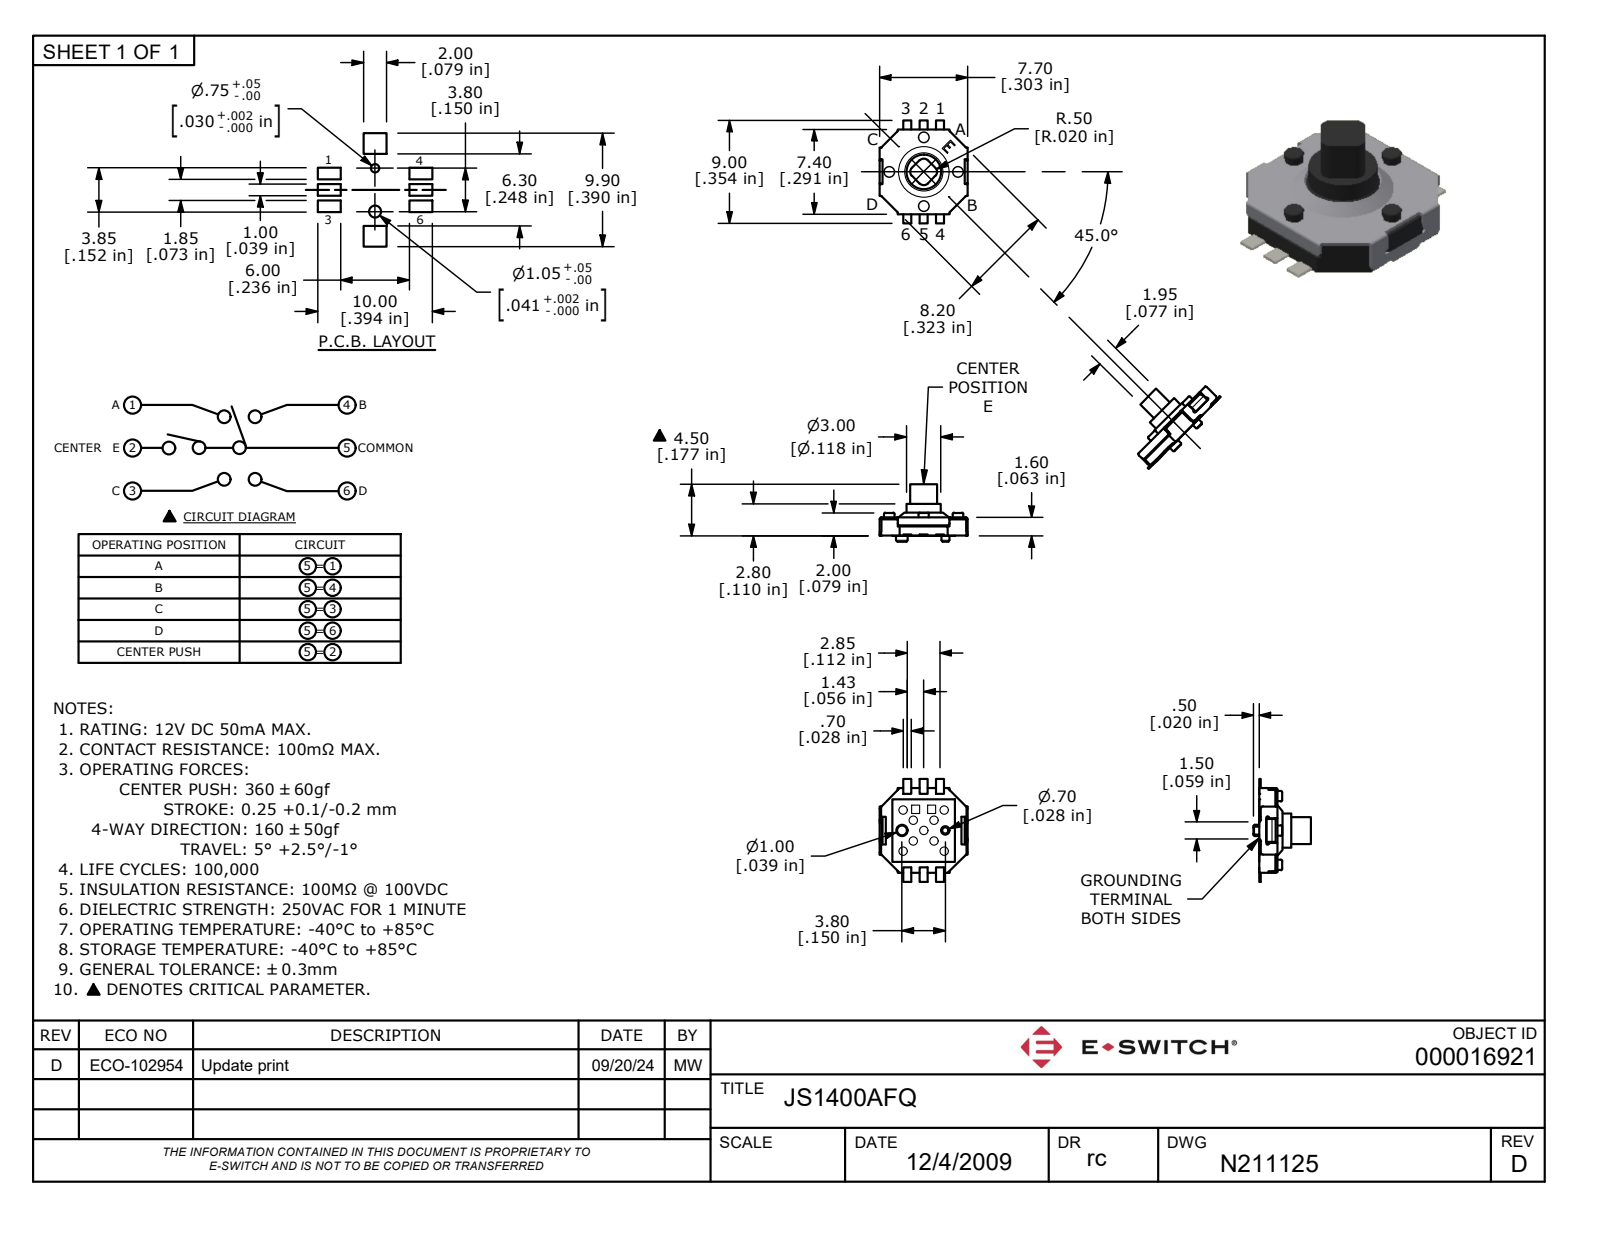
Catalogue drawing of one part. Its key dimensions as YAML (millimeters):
part_name: "P:\\\\E-Switch Secure\\\\3D_MODELS_STP_FORMAT\\\\JS1400AFQ.stp"
step_written_by: "ACIS (CONFIG_CONTROL_DESIGN)"
units: millimeters
bodies: {solids: 2, faces: 247, planar: 193, cylindrical: 44, other: 10}
overall_size: [9, 7.8, 5]
volume: 80
surface_area: 327
round_holes:
  - {diameter: 0.7, count: 9}
  - {diameter: 0.8, count: 4}
round_bosses_or_shafts:
  - {diameter: 0.7, count: 5}
  - {diameter: 0.9, count: 4}
  - {diameter: 3, count: 1}
  - {diameter: 1, count: 1}
partial_cylinders:
  - {radius: 0.5, count: 4}
  - {radius: 1.2, count: 4}
face_to_face_distances: [0.6, 0.4, 0.9, 0.7, 1, 1.6, 1.4, 1.6, 1.4, 0.5]
hole_center_spacings: [1.3, 2.2, 2.3, 2.8, 4, 5.1, 2.5, 1.8]
